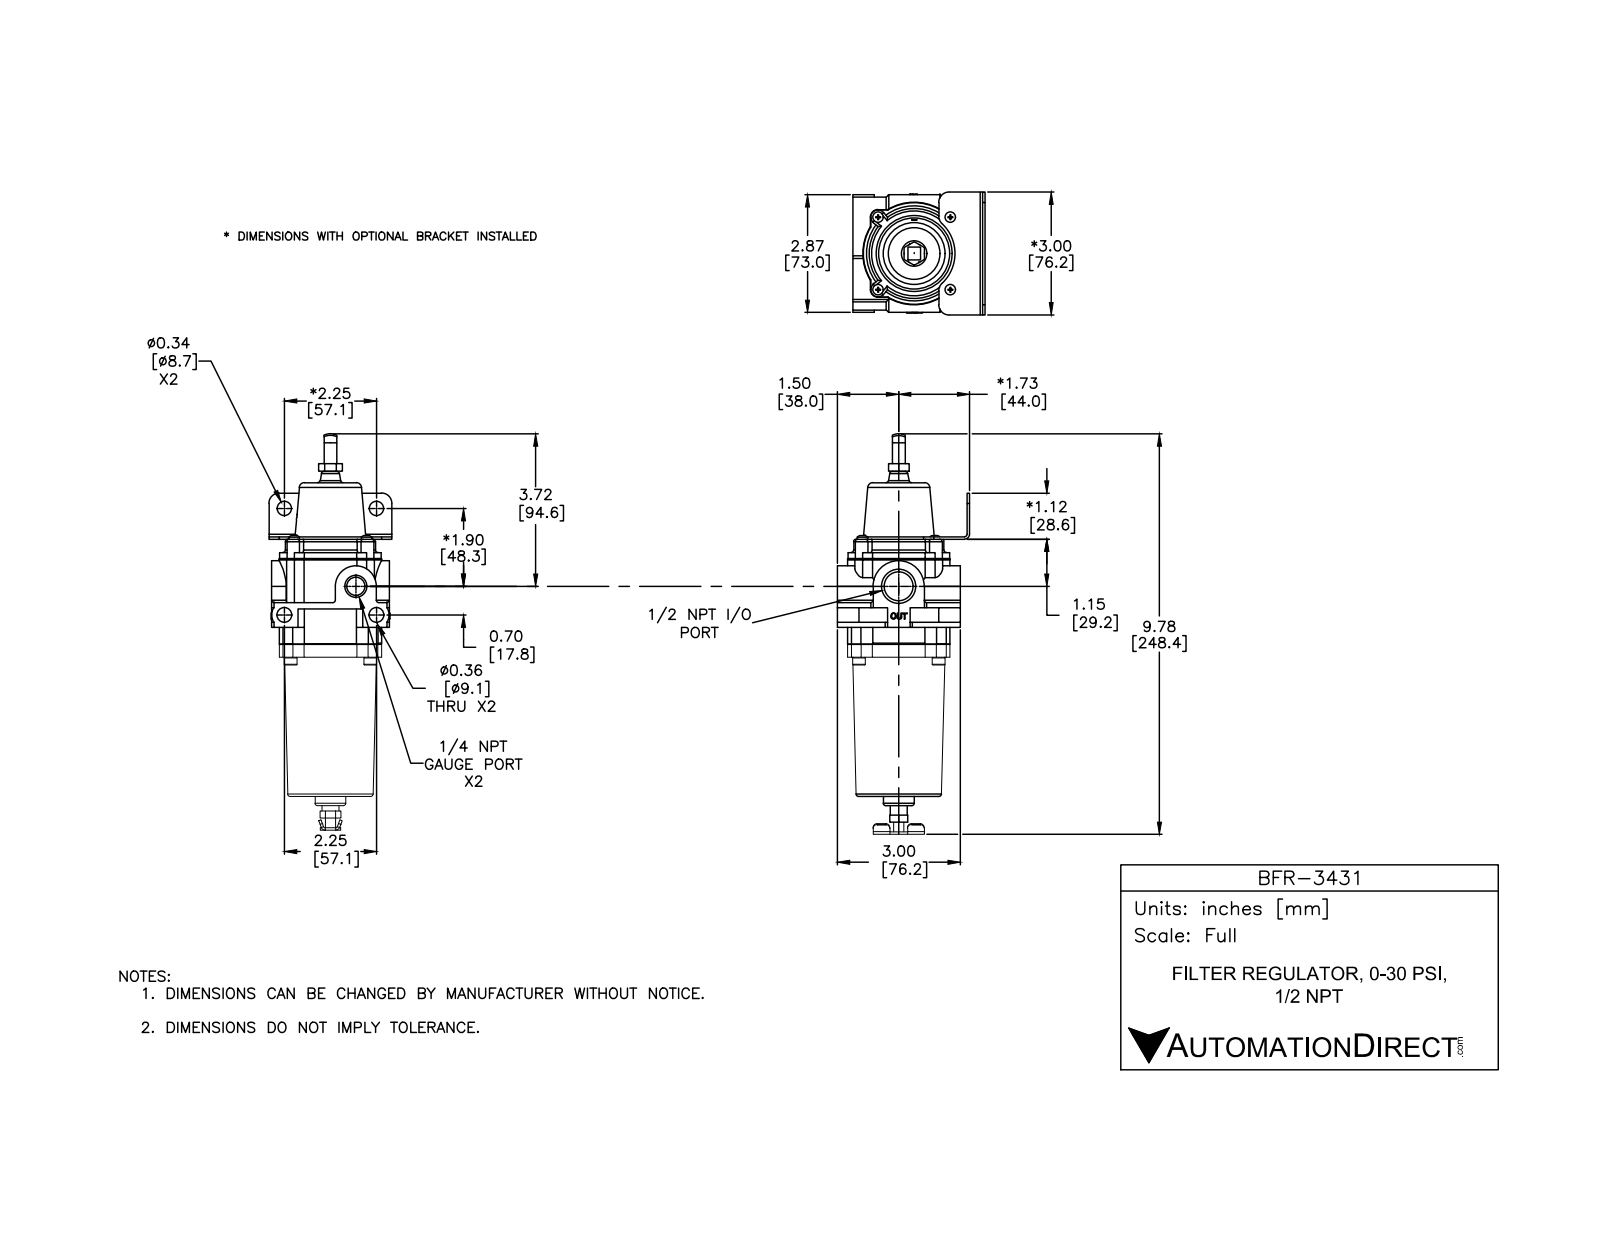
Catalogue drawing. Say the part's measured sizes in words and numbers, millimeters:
The part is named "BFR-3431". Its 3-D file was written by "SolidWorks 2015 (CONFIG_CONTROL_DESIGN)". It is 15 solids with 1577 faces: 336 planar, 1000 cylindrical and 241 other. Overall it measures 248.1 by 76.2 by 73.5 millimeters. Its volume is 348 100 cubic millimeters and its surface area 97 290 square millimeters. Round holes: 8 of diameter 4, 4 of diameter 5.1, 4 of diameter 5.3, 2 of diameter 9.1, 1 of diameter 3.2, 1 of diameter 6.5, 1 of diameter 6.6, 1 of diameter 11.1, 1 of diameter 17.9. Round bosses or shafts: 8 of diameter 4.8, 8 of diameter 3.8, 5 of diameter 7.9, 4 of diameter 9.5, 1 of diameter 54.4, 1 of diameter 19.1, 1 of diameter 13, 1 of diameter 10.6. Partial cylindrical surfaces (rounded edges, fillets, slot ends): 48 of radius 0.1, 12 of radius 4.8, 8 of radius 2.5, 6 of radius 0.5, 5 of radius 1.6, 5 of radius 1.6, 4 of radius 4.7, 2 of radius 1. The main face-to-face distances are 52.7, 94.4, 147.1, 3.6, 90.8, 143.5, 104.9, 101.3, 10.5, 42.2. The hole center spacings are 47.2, 3.2, 49.4, 34.9, 31.8, 31.8, 44.9, 44.9.
